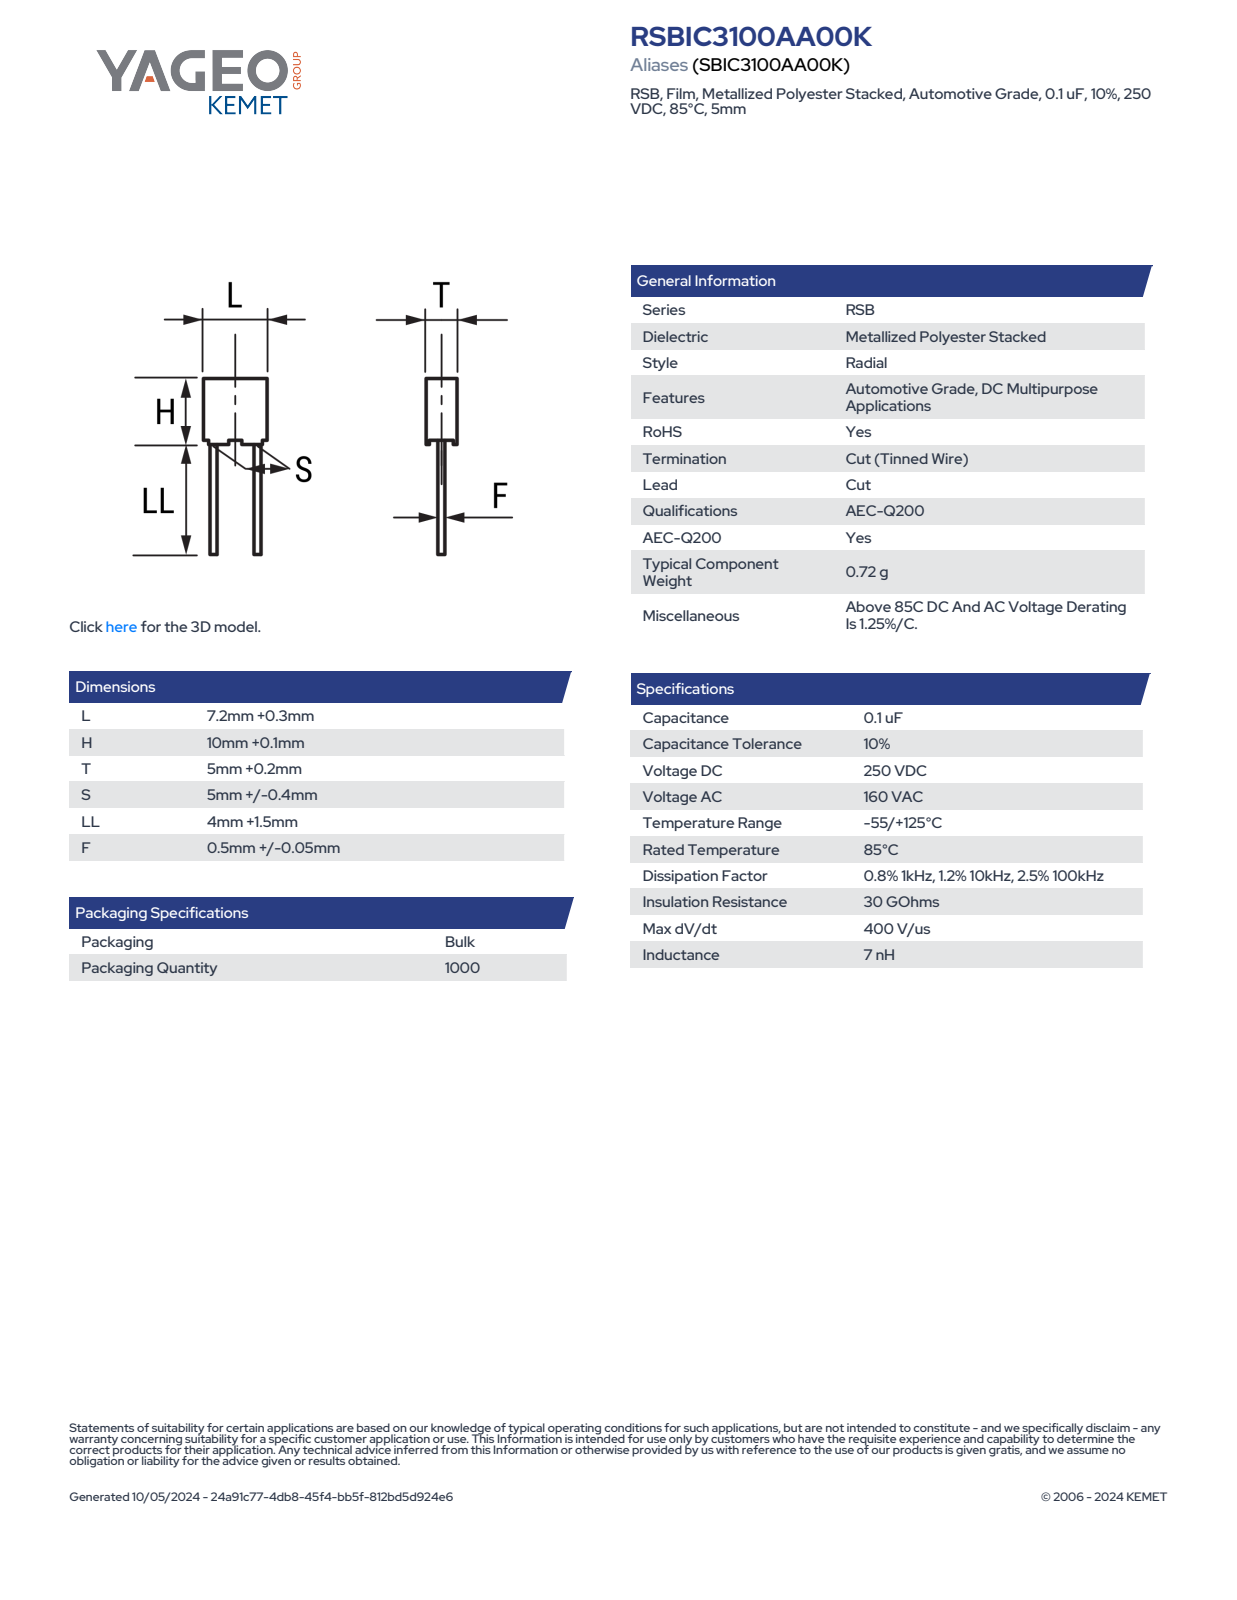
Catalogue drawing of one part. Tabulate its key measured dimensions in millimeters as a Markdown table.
| quantity | value |
| --- | --- |
| part name | CFR_RB3_7.2X10X5_L7.5H10.1T5.2S5LL5.5F0.65 |
| STEP written by | SolidWorks 2014 (AUTOMOTIVE_DESIGN) |
| units | millimeters |
| bodies | 4 solids, 85 faces (77 planar, 8 cylindrical, 0 other) |
| overall size | 15.6 × 7.5 × 5.21 |
| volume | 372 mm³ |
| surface area | 374 mm² |
| round bosses / shafts (diameter × count) | 0.65 × 2 |
| partial cylindrical surfaces (radius × count) | 0.5 × 4 |
| main face-to-face distances | 5.2, 7.5, 9.35, 4.95, 7.25, 0.75, 10.1, 4.7, 7, 0.35 |
